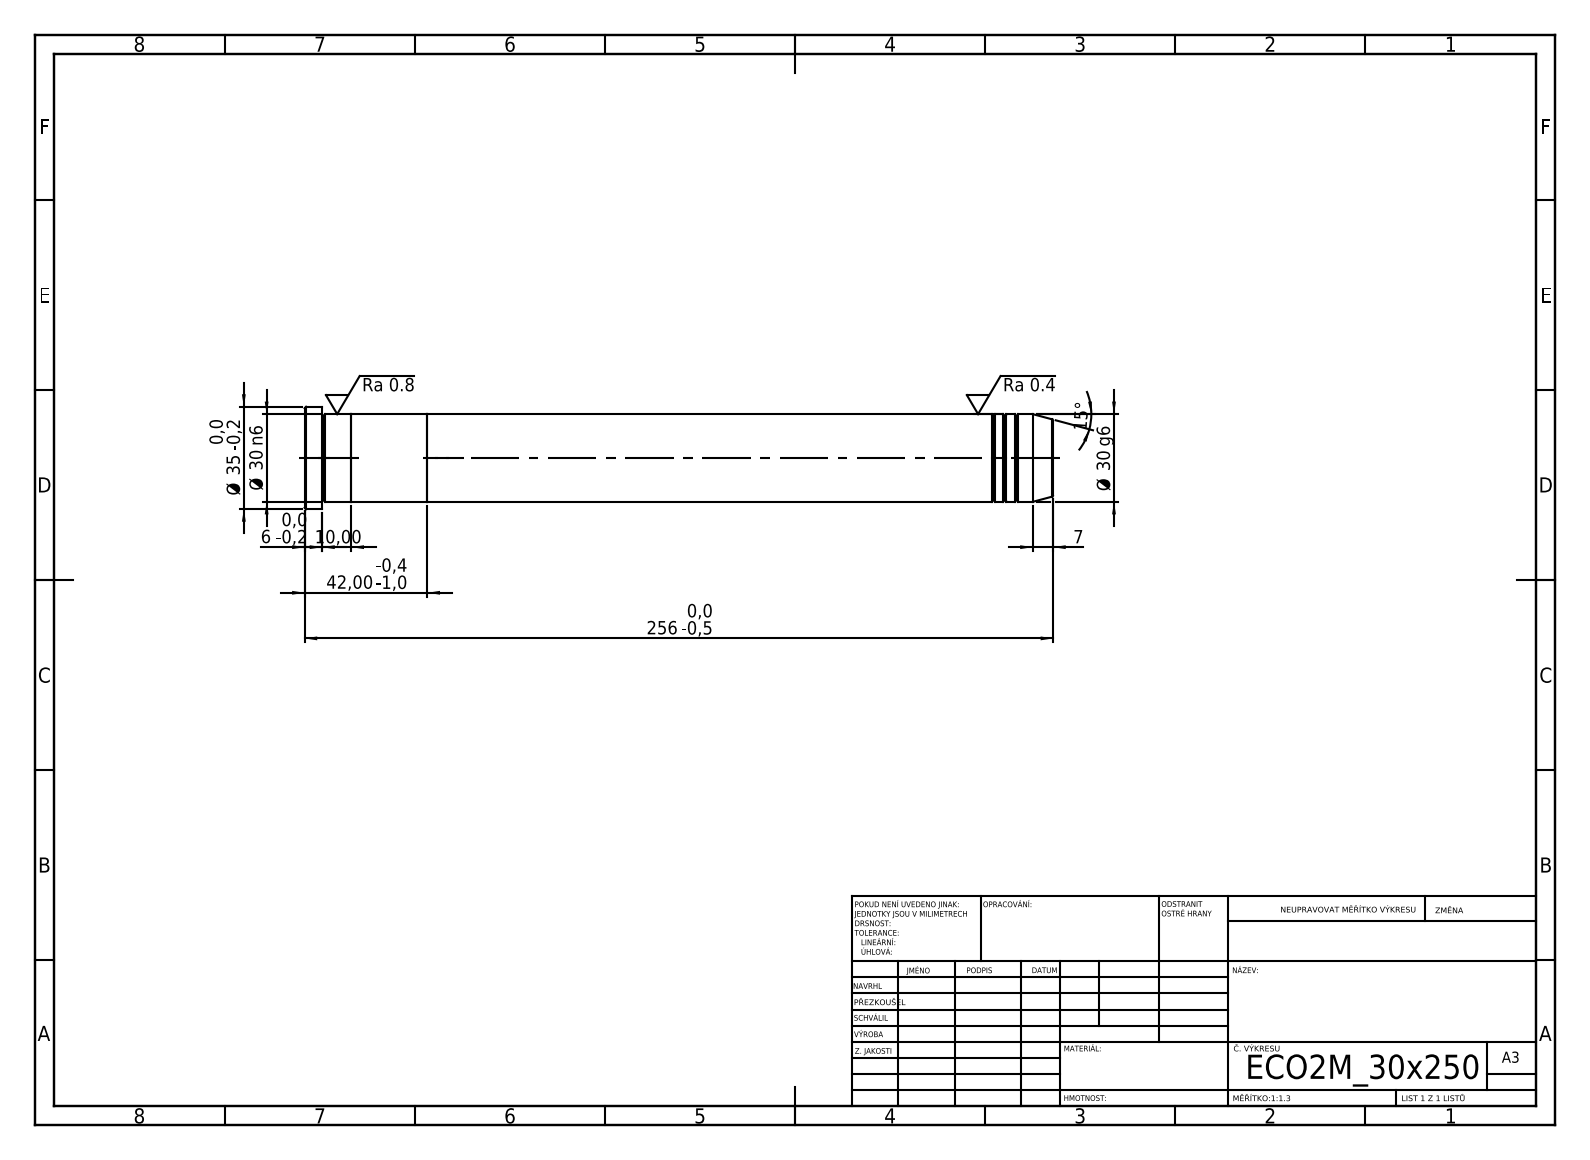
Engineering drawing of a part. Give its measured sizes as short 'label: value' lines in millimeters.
written by: SolidWorks 2019 (CONFIG_CONTROL_DESIGN)
unit: mm
bodies: 3 solids, 43 faces (7 planar, 14 cylindrical, 22 other)
size: 256 × 35 × 35
volume: 181 732 mm³; area: 28 949 mm²
bosses: 1× ⌀35, 1× ⌀30
face distances: 26, 42, 16, 214, 240, 256, 250, 36, 10, 6
